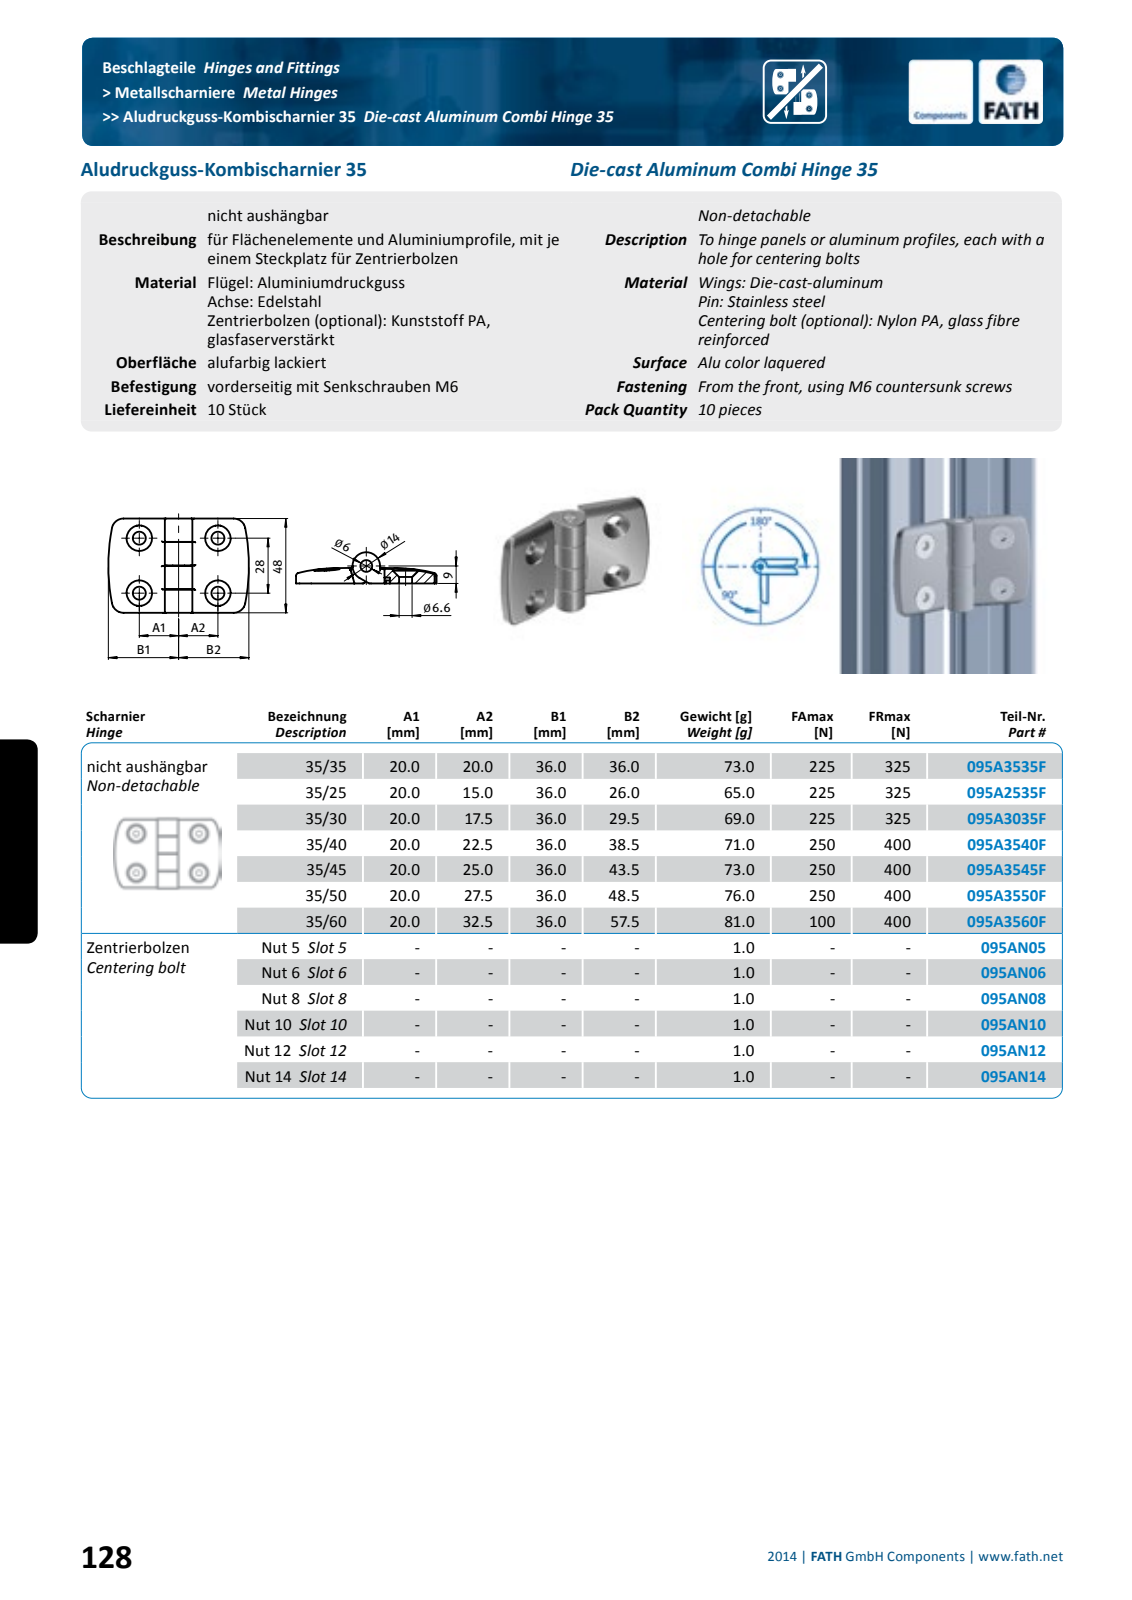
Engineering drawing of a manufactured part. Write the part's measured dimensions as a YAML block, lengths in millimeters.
part_name: "fath_095a3535f_1; fath_095a3535f_2; fath_095a3535f_3; fath_095a3535f_4 (+1 more)"
step_written_by: "Spatial InterOp 3D (automotive_design)"
units: millimeters
bodies: {solids: 5, faces: 678, planar: 250, cylindrical: 194, other: 234}
overall_size: [71.5, 48, 18.25]
volume: 24100
surface_area: 13859
round_holes:
  - {diameter: 6, count: 1}
round_bosses_or_shafts:
  - {diameter: 14, count: 1}
partial_cylinders:
  - {radius: 0.5, count: 54}
  - {radius: 0.3, count: 22}
  - {radius: 0.2, count: 20}
  - {radius: 6, count: 4}
  - {radius: 6.5, count: 4}
  - {radius: 4, count: 2}
  - {radius: 100, count: 2}
  - {radius: 3.1, count: 1}
face_to_face_distances: [11.9, 36.1, 3, 12, 2.8, 12.2, 23.9, 24.1, 24.2, 48]
